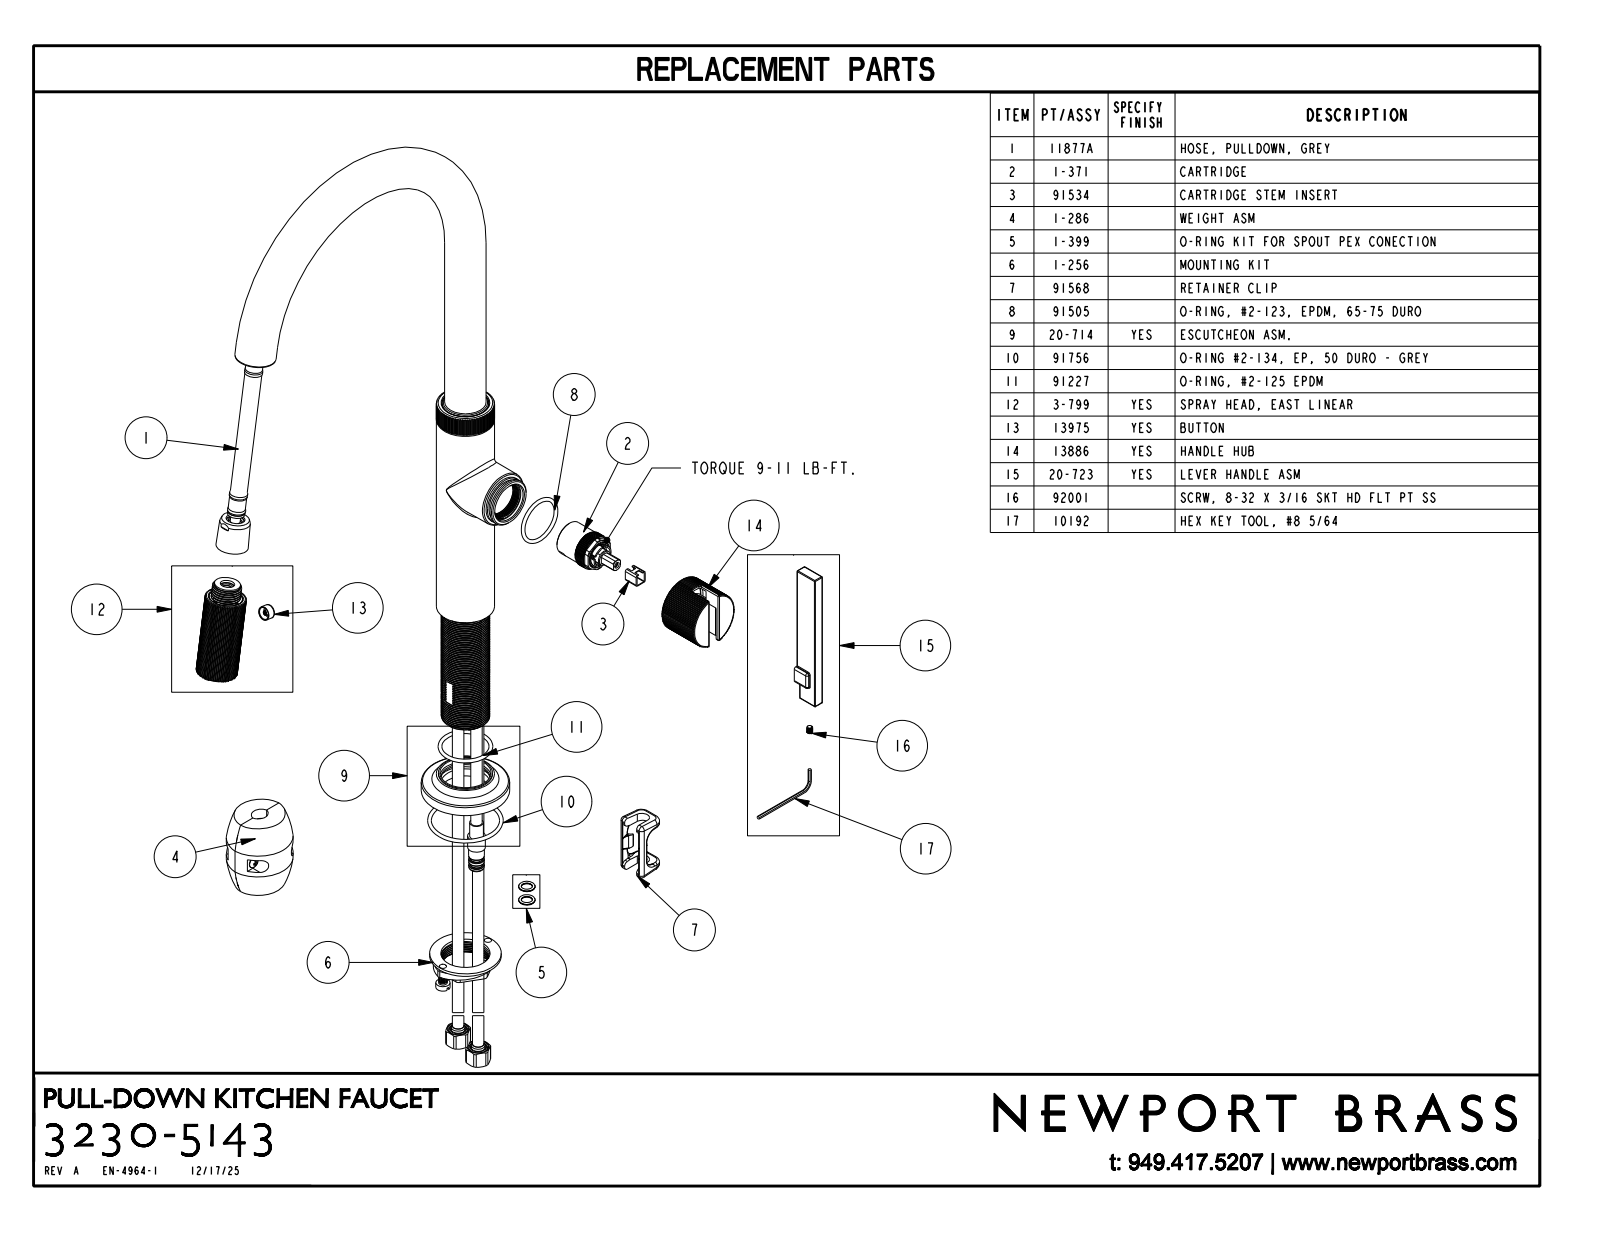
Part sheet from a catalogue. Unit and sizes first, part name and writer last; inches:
Units: inches
Overall size (bounding box): 17.442 × 10.301 × 3.972
Round holes (diameter × count): ⌀0.039 ×48, ⌀0.598 ×2, ⌀0.638 ×2, ⌀0.135 ×1, ⌀0.21 ×1, ⌀0.236 ×1, ⌀0.394 ×1, ⌀0.472 ×1, ⌀0.52 ×1, ⌀0.559 ×1, ⌀0.591 ×1, ⌀0.82 ×1
Round bosses / shafts (diameter × count): ⌀0.102 ×18, ⌀0.079 ×18, ⌀0.551 ×2, ⌀2.43 ×1, ⌀1.6 ×1, ⌀1.49 ×1, ⌀1.354 ×1, ⌀1.28 ×1
Partial cylindrical surfaces — rounded edges, fillets, slot ends (radius × count): R0.02 ×52, R0.008 ×21, R0.02 ×19, R0.039 ×16, R0.012 ×8, R0.06 ×8, R0.125 ×6, R0.01 ×4
Main face-to-face distances: 0.3, 0.015, 0.713, 0.315, 0.55, 6.86, 0.59, 0.58, 0.35, 6.28
Hole centre spacings: 0.364, 0.364, 0.365, 0.487, 0.076, 0.225, 0.541, 0.724
Volume: 42.29 in³ · Surface area: 210.7 in²
Bodies: 18 solids, 2712 faces (1592 planar, 831 cylindrical, 289 other)
Part name (STEP PRODUCT): 13824; 13672; 91712; 13385 (+8 more)
STEP written by: CREO PARAMETRIC BY PTC INC, 2023134 (CONFIG_CONTROL_DESIGN)
